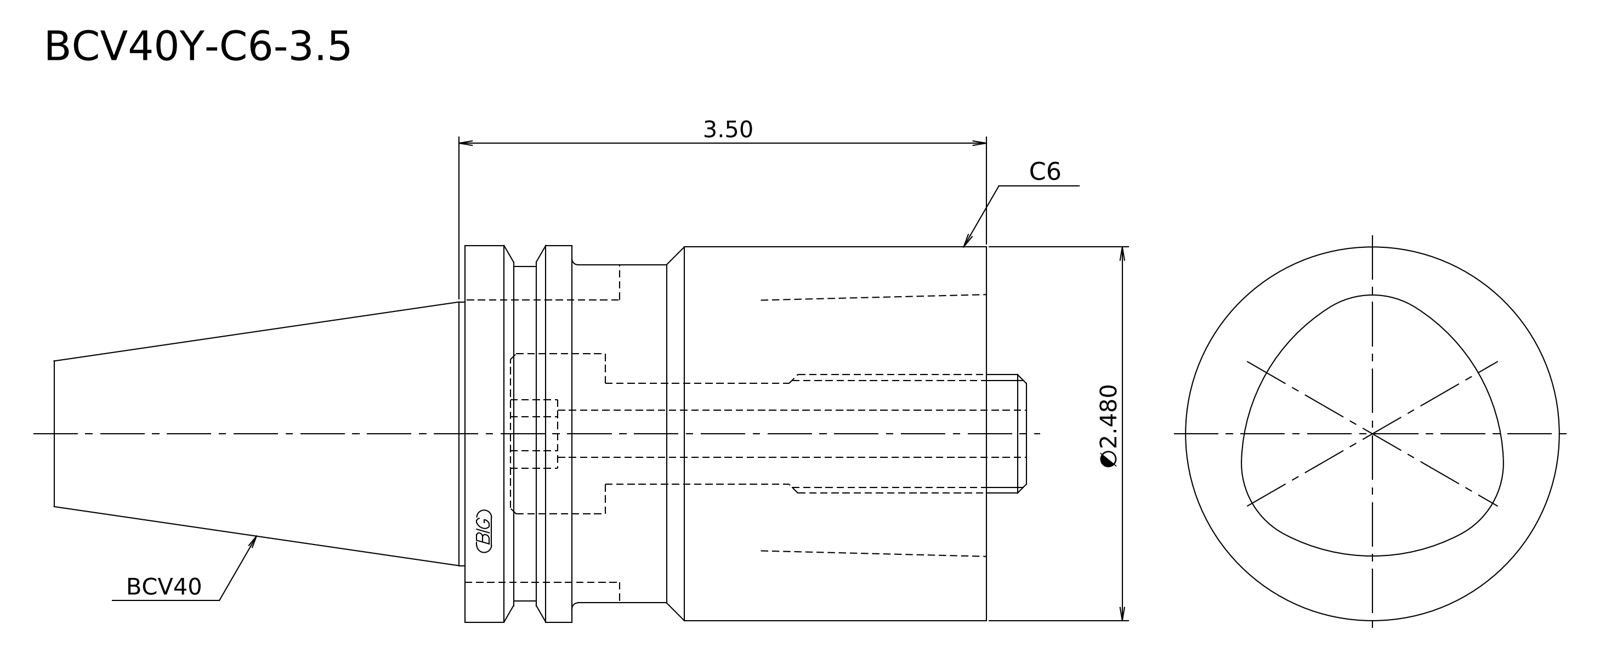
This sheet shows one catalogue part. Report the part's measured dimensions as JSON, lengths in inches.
{"step_written_by": "Kubotek KeyCreator 2011 V10.0.2 (22737) (automotive_design)", "units": "inches", "bodies": {"solids": 1, "faces": 16, "planar": 6, "cylindrical": 6, "other": 4}, "overall_size": [6.187, 2.5, 2.5], "volume_in3": 20.06, "surface_area_in2": 48.9, "round_bosses_or_shafts": [[2.5, 1], [2.48, 1], [2.244, 1], [2.219, 1], [1.75, 1]], "face_to_face_distances": [3.461, 2.75, 0.711, 6.187, 3.437, 2.726, 3.138, 0.388, 0.323, 3.049]}
